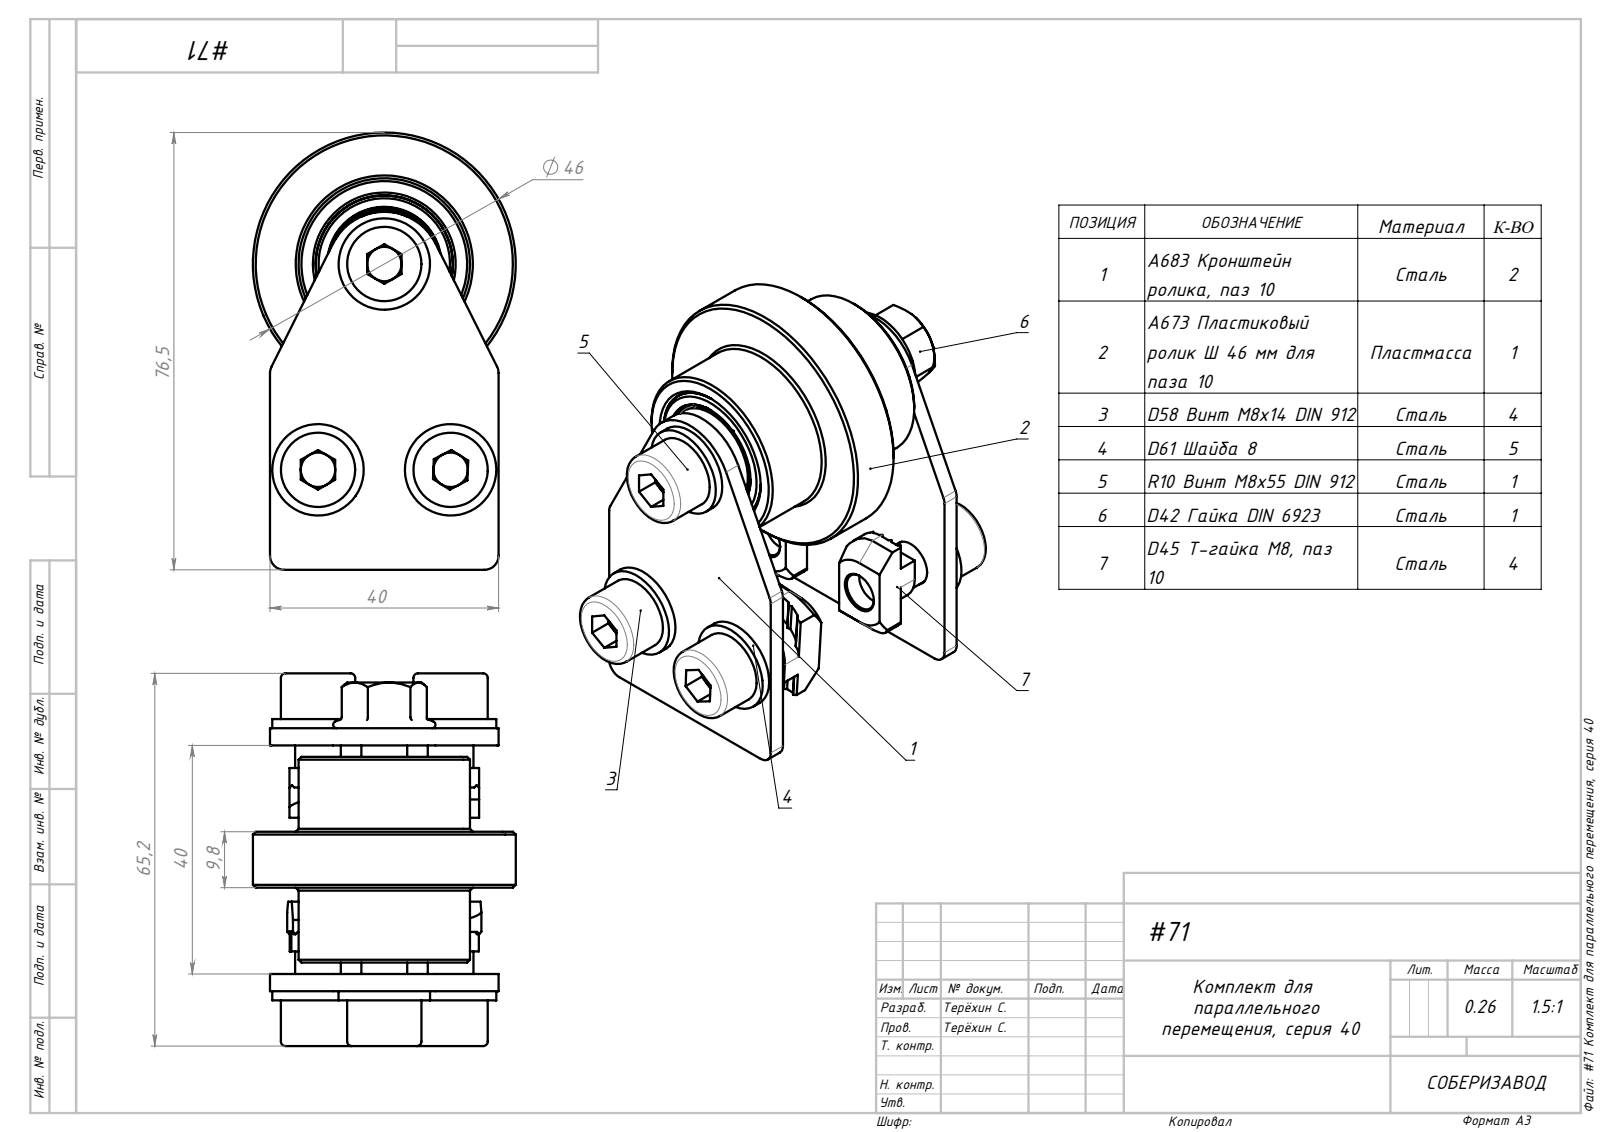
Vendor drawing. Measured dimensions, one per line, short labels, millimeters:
name: A683 Кронштейн ролика, паз 10_00; A673 Пластиковый ролик Ø 46 мм для паза 10_00; D42 Гайка DIN 6923_00; D58 Винт M8x14 DIN 912_00 (+4 more)
written by: SolidWorks 2022 (AUTOMOTIVE_DESIGN)
unit: mm
bodies: 24 solids, 679 faces (421 planar, 126 cylindrical, 132 other)
size: 76.5 × 65.2 × 46
volume: 54 778 mm³; area: 36 902 mm²
holes: 3× ⌀8.2, 3× ⌀8.4, 2× ⌀6.7, 1× ⌀6.8, 1× ⌀8, 1× ⌀12.2, 1× ⌀20, 1× ⌀24
bosses: 3× ⌀16, 3× ⌀13, 2× ⌀8, 1× ⌀46, 1× ⌀30, 1× ⌀19.8, 1× ⌀12
rounds: 8× R5.67, 8× R6, 4× R2.5, 1× R10
face distances: 43, 3, 46, 40, 27.9, 18.1, 15.1, 24.9, 1.6, 4.6
hole spacings: 37.82, 23.2
